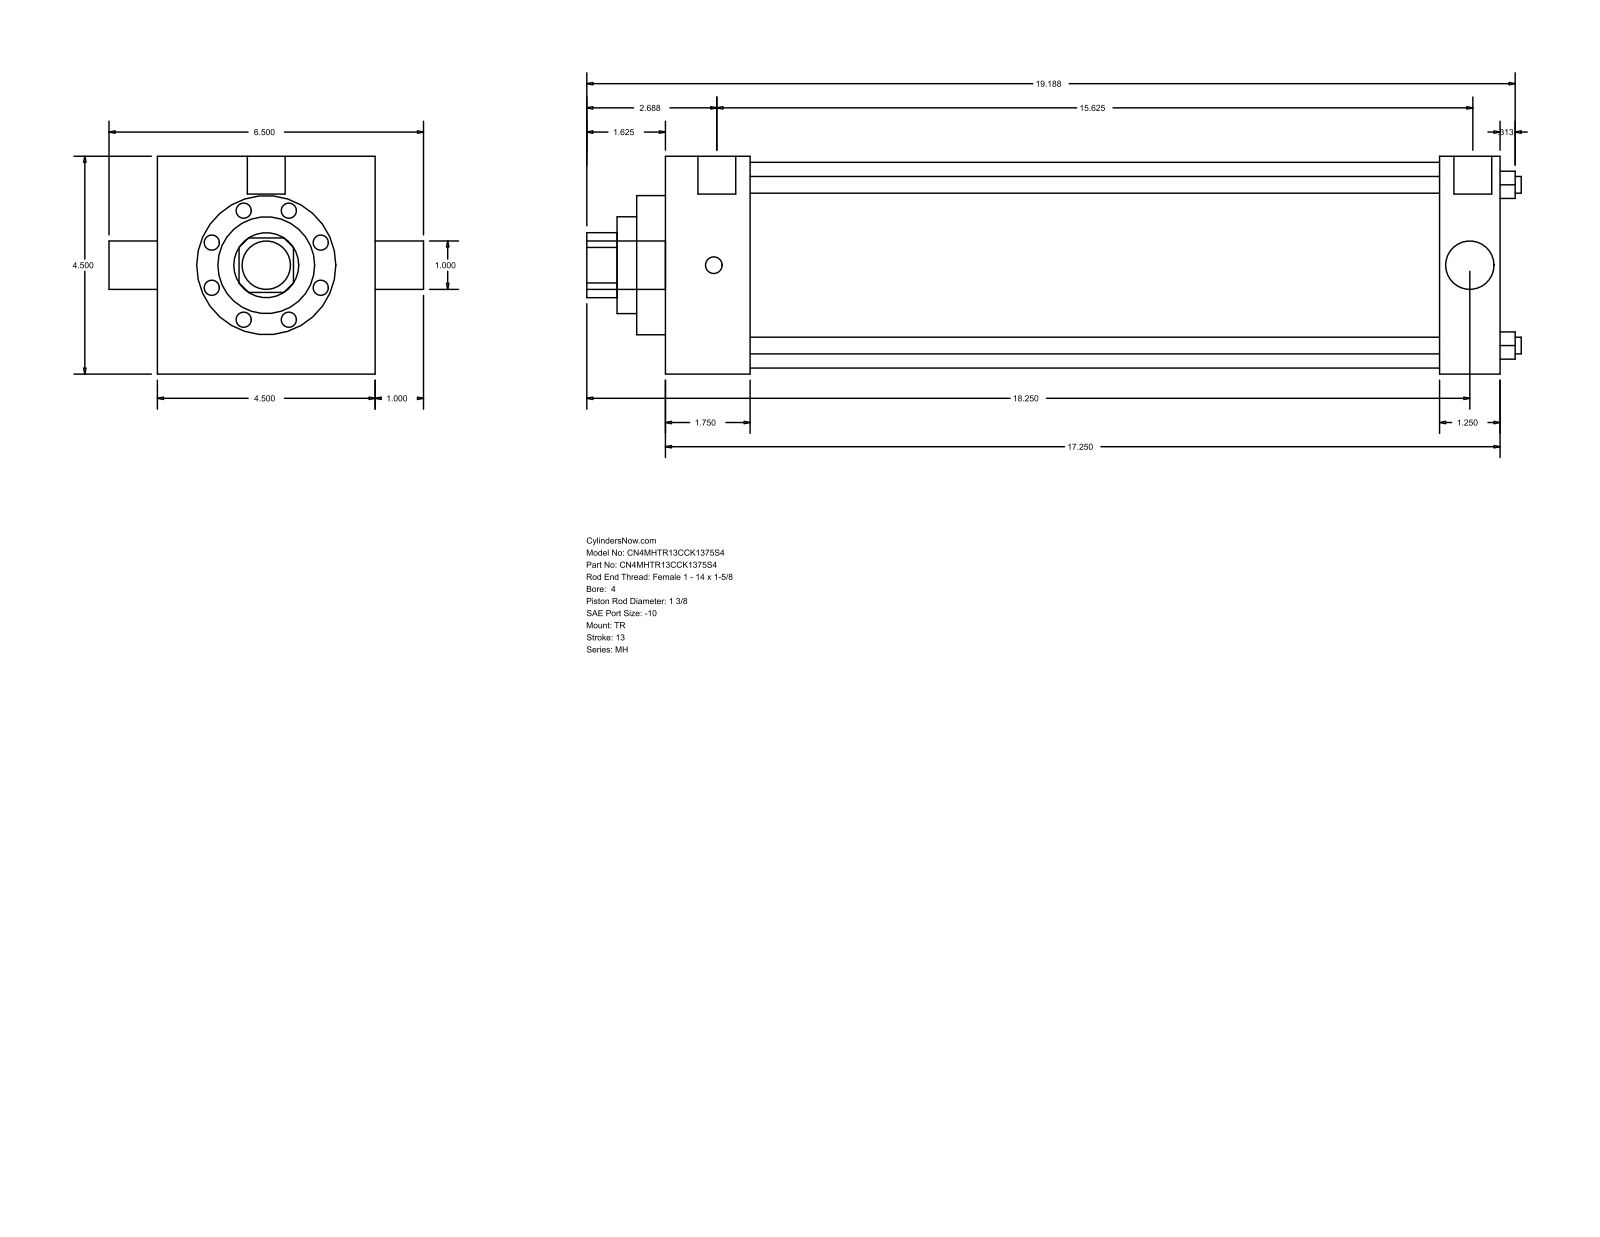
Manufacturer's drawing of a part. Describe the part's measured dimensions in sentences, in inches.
The part is named "MH_TR__0400_1.375". Its 3-D file was written by "GSSL Pune (CONFIG_CONTROL_DESIGN)". It is 0 solids with 86 faces: 61 planar, 25 cylindrical and 0 other. Overall it measures 19.313 by 6.5 by 4.5 inches. Round holes: 4 of diameter 0.345, 1 of diameter 1, 1 of diameter 1.375, 1 of diameter 2, 1 of diameter 2.875, 1 of diameter 4.25. Round bosses or shafts: 3 of diameter 0.344, 2 of diameter 0.781, 1 of diameter 1. Partial cylindrical surfaces (rounded edges, fillets, slot ends): 1 of radius 0.672. The main face-to-face distances are 4.5, 17.25, 1.75, 15.5, 16, 14.25, 1.25, 0.594, 2.344, 16.594. The hole center spacings are 2.347, 3.32, 4.695.
